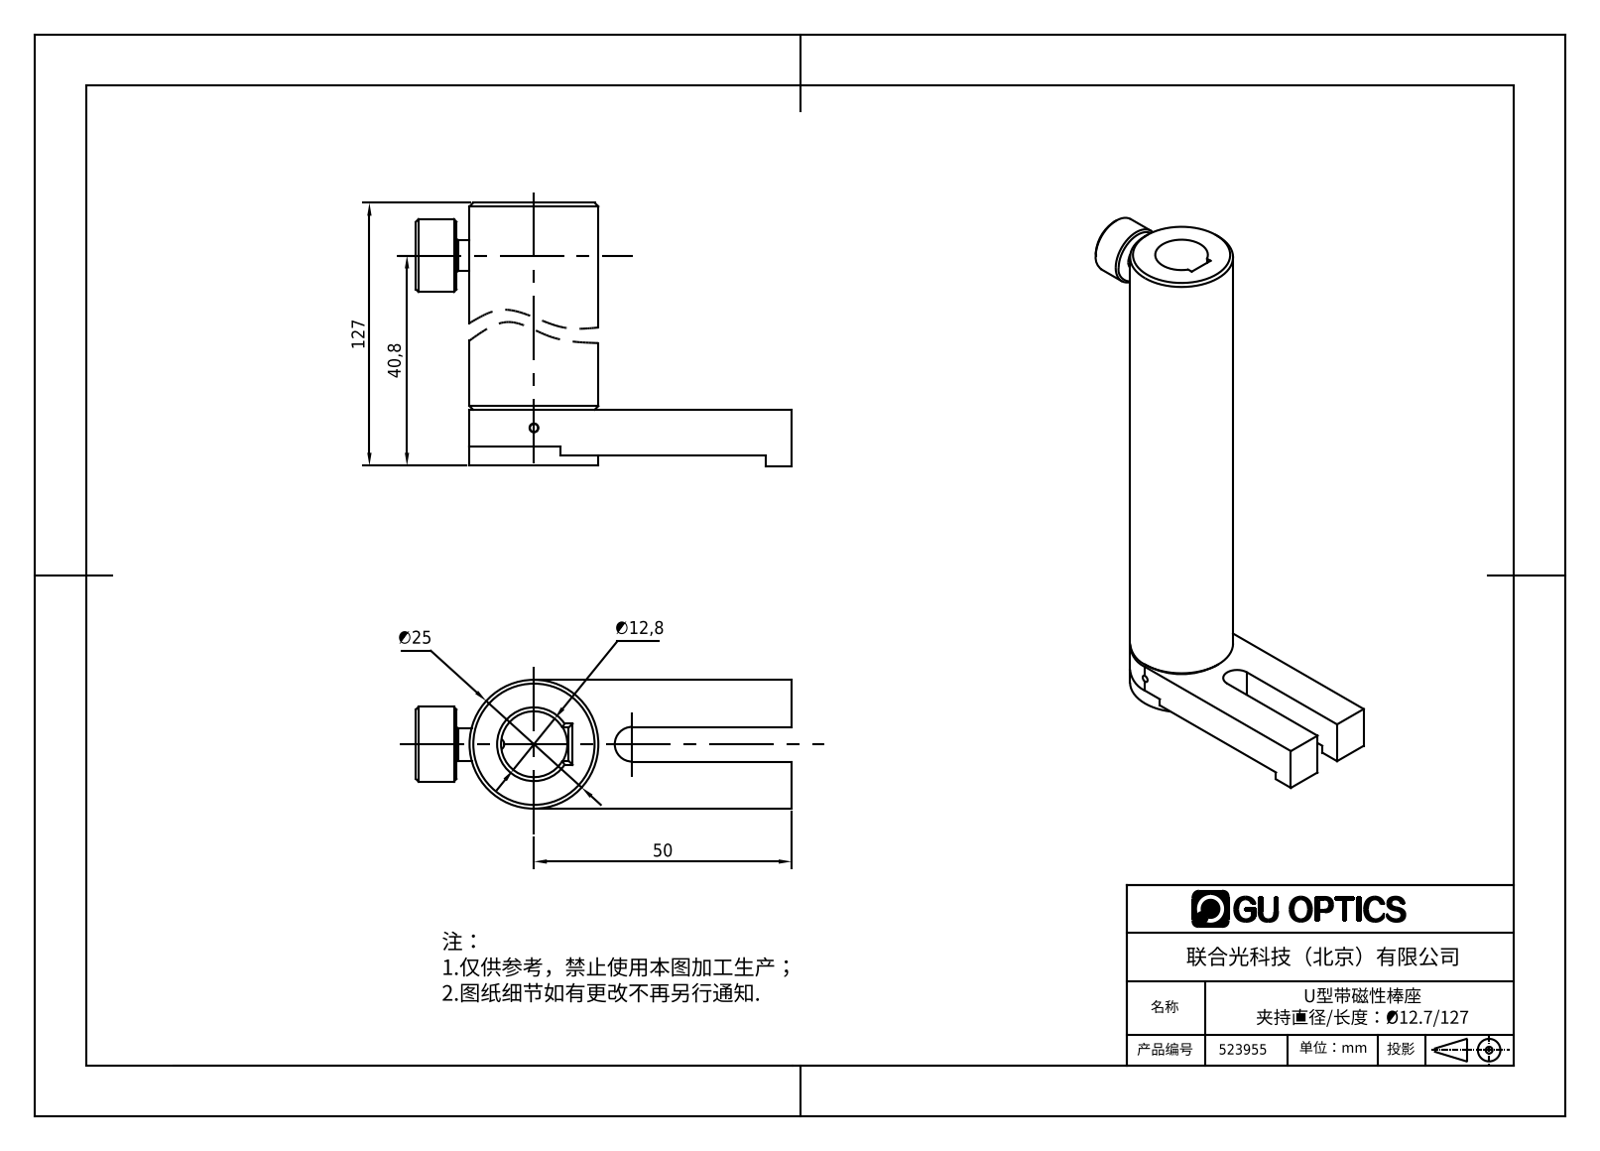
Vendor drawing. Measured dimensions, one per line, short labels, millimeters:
name: 523955
written by: SolidWorks 2016 (CONFIG_CONTROL_DESIGN)
unit: mm
bodies: 8 solids, 128 faces (38 planar, 50 cylindrical, 40 other)
size: 127.05 × 72.91 × 24.99
volume: 54 521 mm³; area: 22 927 mm²
holes: 3× ⌀4.83, 1× ⌀1.59, 1× ⌀1.7, 1× ⌀1.78, 1× ⌀12.78, 1× ⌀12.95, 1× ⌀20.09
bosses: 3× ⌀4.76, 1× ⌀24.99, 1× ⌀20.05, 1× ⌀17.78, 1× ⌀17.27, 1× ⌀14.12, 1× ⌀5.99, 1× ⌀3
rounds: 1× R3.37, 1× R12.95
face distances: 8.89, 9.13, 15.87, 25, 1.83, 7.06, 1.98, 3.81, 10.87, 127
hole spacings: 16.5, 9.53, 9.52
